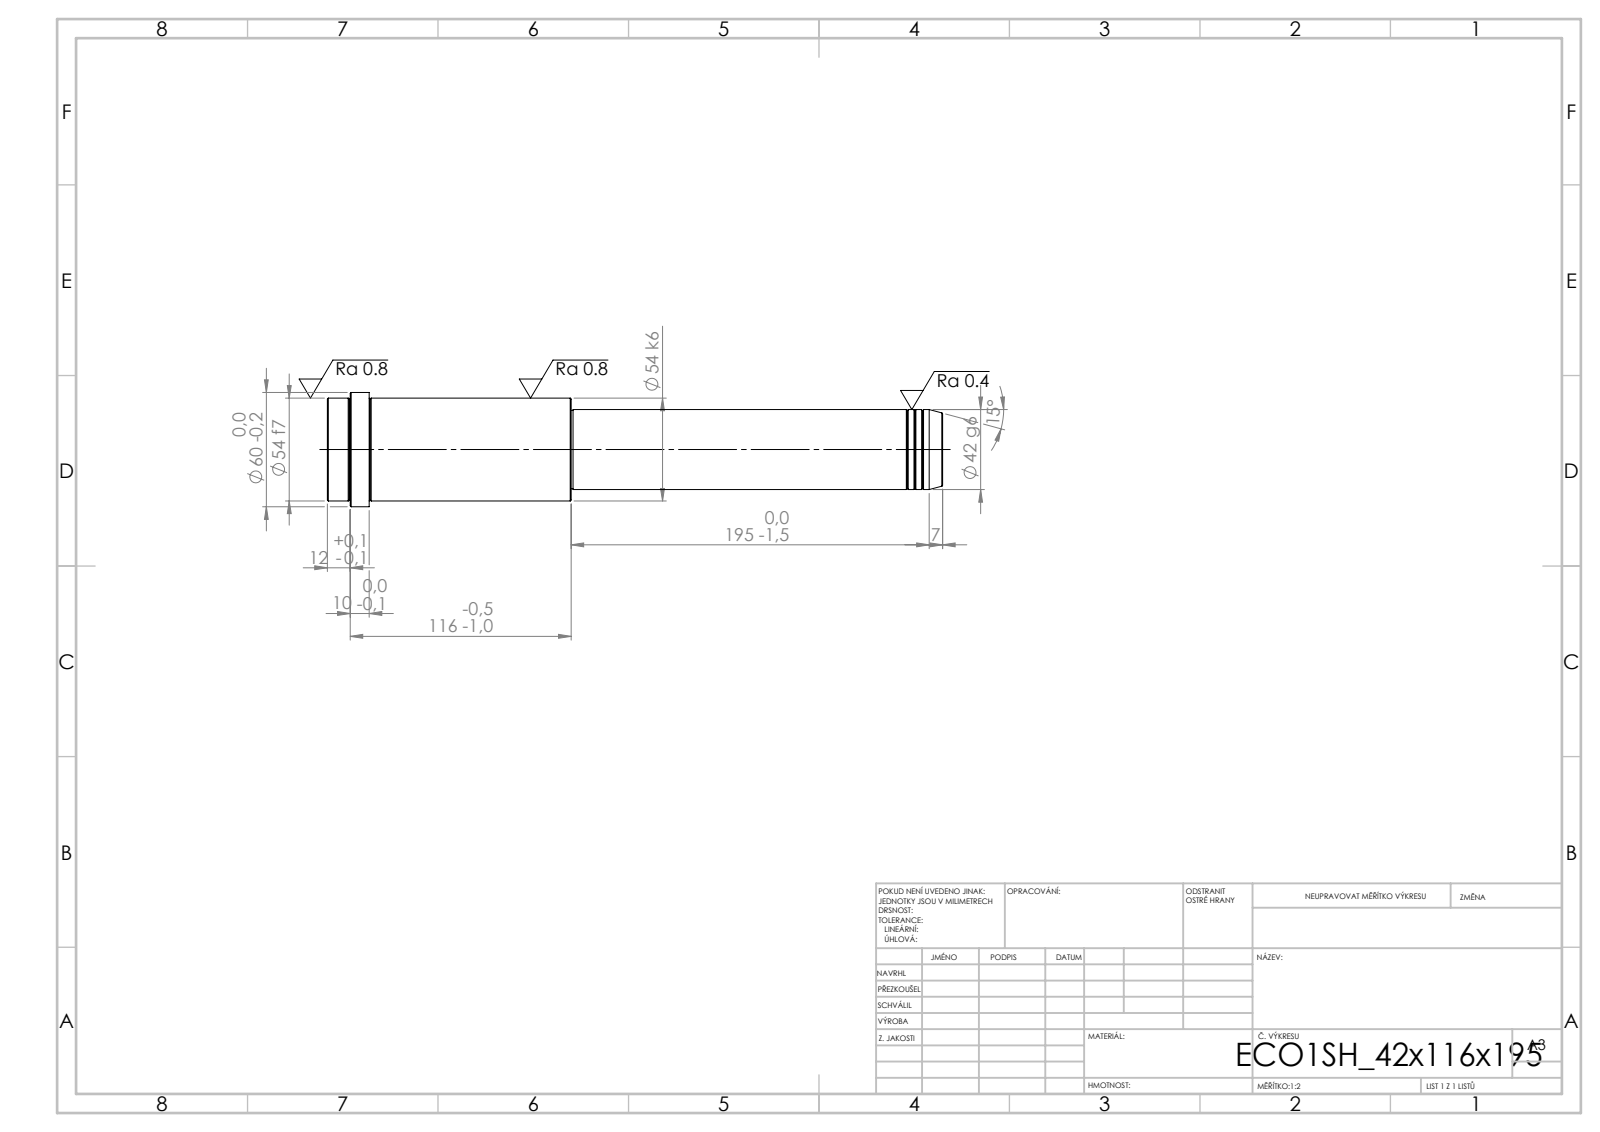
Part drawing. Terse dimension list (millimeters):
written by: SolidWorks 2019 (CONFIG_CONTROL_DESIGN)
unit: mm
bodies: 1 solid, 52 faces (6 planar, 16 cylindrical, 30 other)
size: 323 × 60 × 60
volume: 567 421 mm³; area: 53 403 mm²
bosses: 1× ⌀60, 1× ⌀54, 1× ⌀42, 1× ⌀41
face distances: 323, 195, 128, 301, 106, 22, 311, 116, 10, 12
